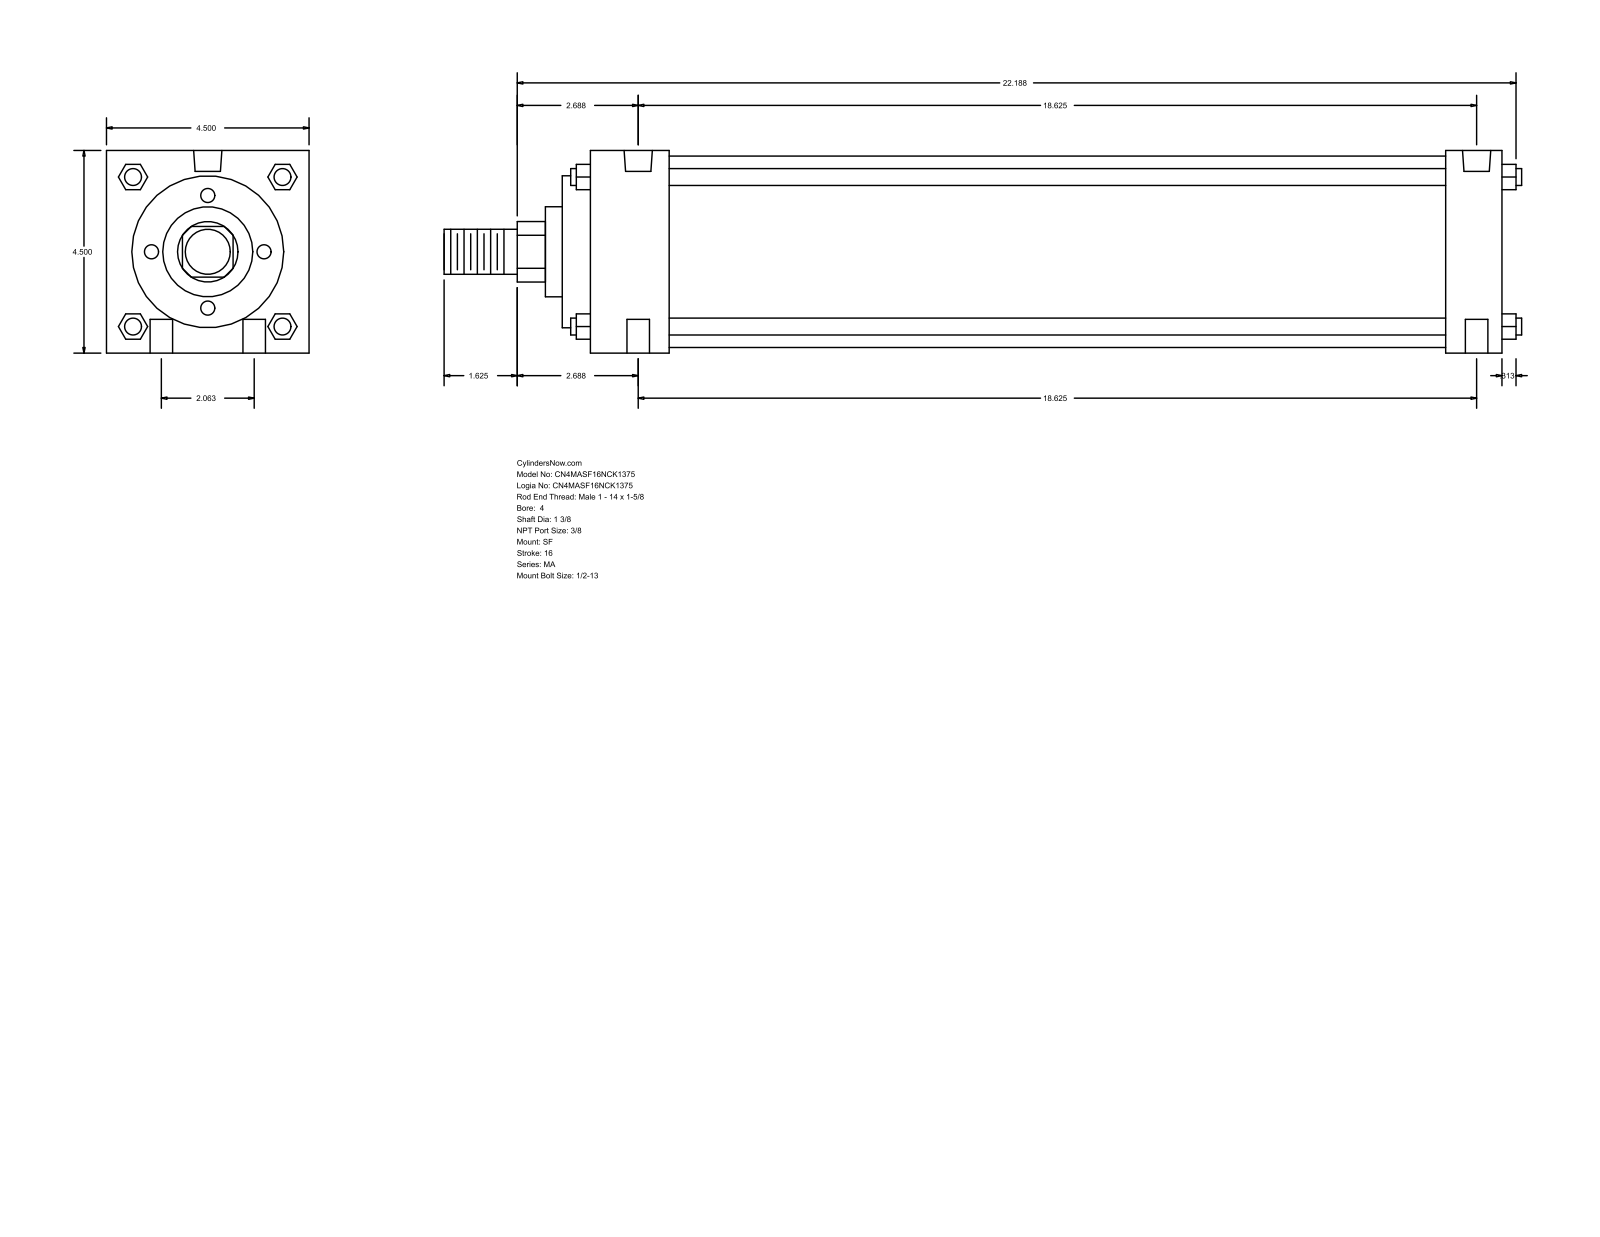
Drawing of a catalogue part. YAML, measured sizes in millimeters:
part_name: "MA_SF__0400_1.375"
step_written_by: "GSSL Pune (CONFIG_CONTROL_DESIGN)"
units: millimeters
bodies: {solids: 0, faces: 126, planar: 95, cylindrical: 31, other: 0}
overall_size: [608.01, 114.3, 114.3]
round_holes:
  - {diameter: 12.7, count: 4}
  - {diameter: 11.11, count: 2}
  - {diameter: 15.93, count: 2}
round_bosses_or_shafts:
  - {diameter: 9.53, count: 4}
  - {diameter: 107.95, count: 1}
  - {diameter: 85.72, count: 1}
  - {diameter: 50.8, count: 1}
  - {diameter: 34.92, count: 1}
  - {diameter: 25.4, count: 1}
partial_cylinders:
  - {radius: 17.06, count: 1}
face_to_face_distances: [114.3, 514.35, 530.22, 15.87, 498.48, 482.61, 31.74, 60.32, 44.45, 438.16]
hole_center_spacings: [26.19, 473.8, 473.08, 52.38, 475.97, 463.55]
